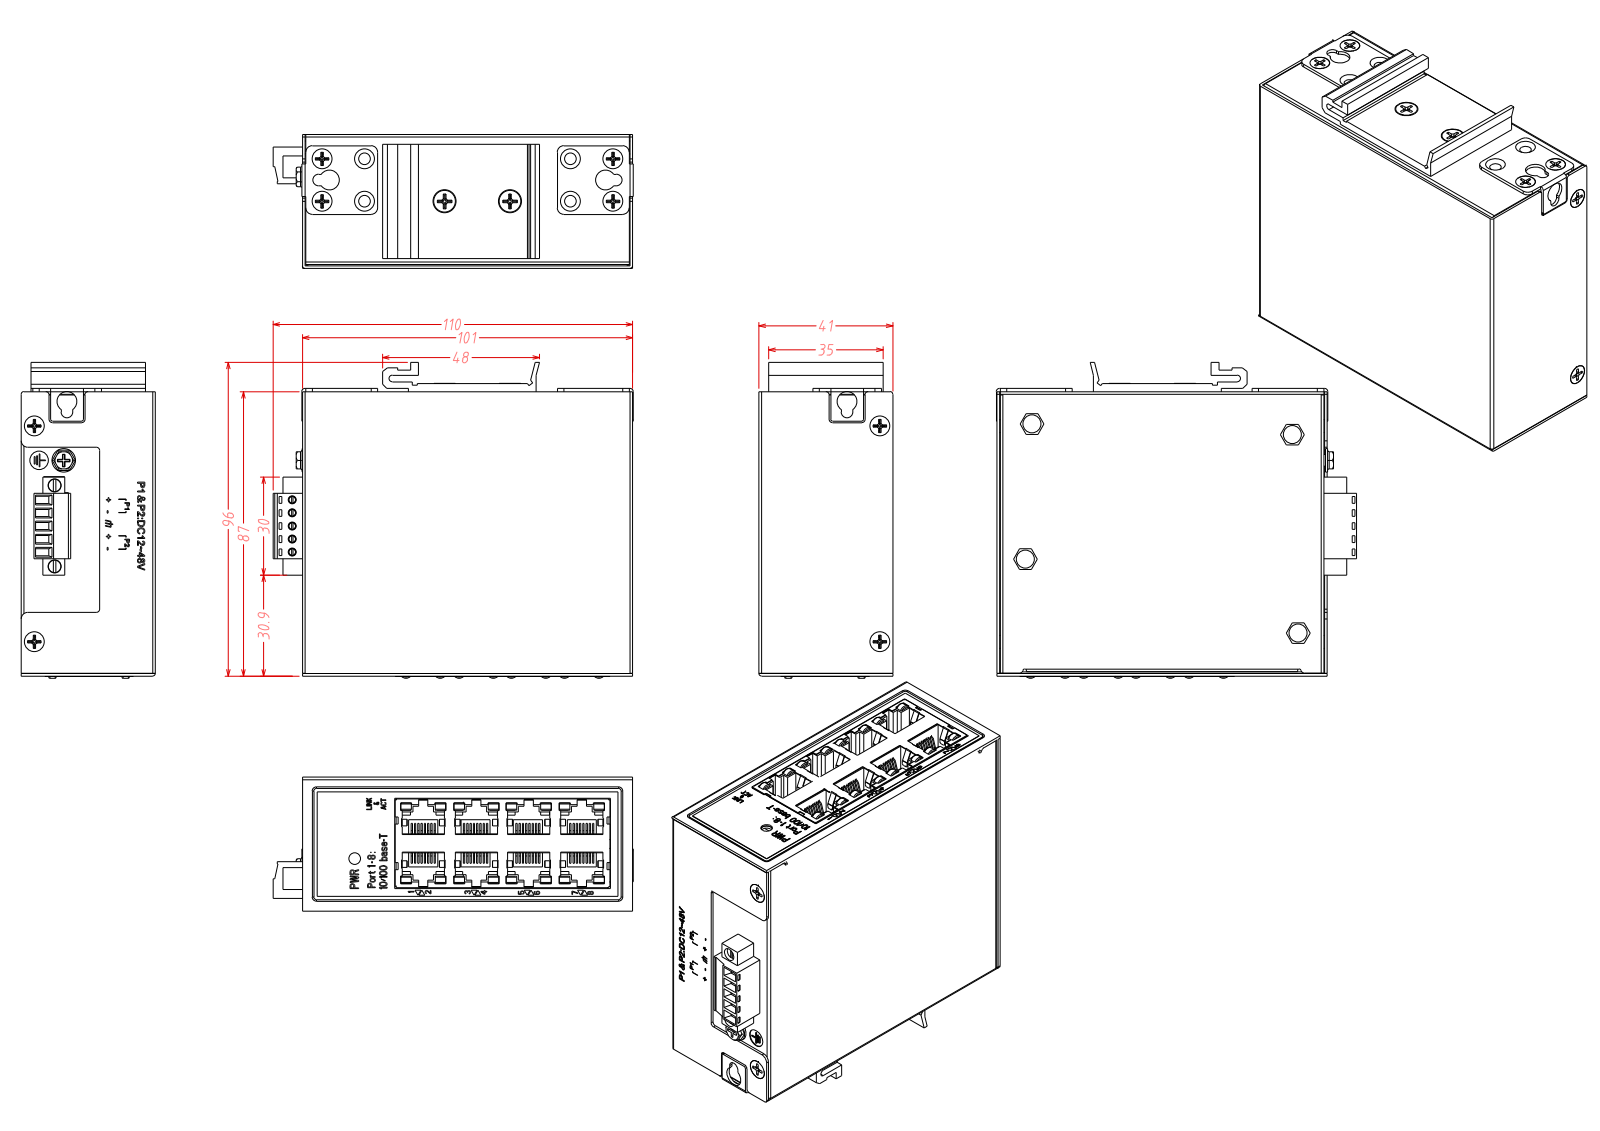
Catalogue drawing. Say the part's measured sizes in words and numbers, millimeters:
The part is named "PRT0123; PRT0124; PRT0125; PRT0126 (+8 more)". Its 3-D file was written by "PRO/ENGINEER BY PARAMETRIC TECHNOLOGY CORPORATION, 2011310 (CONFIG_CONTROL_DESIGN)". It is 41 solids with 3713 faces: 3101 planar, 418 cylindrical and 194 other. Overall it measures 110.2 by 96.68 by 41 millimeters. Its volume is 52 505 cubic millimeters and its surface area 104 092 square millimeters. Round holes: 13 of diameter 2.5, 5 of diameter 2.4, 4 of diameter 5.5, 3 of diameter 6, 2 of diameter 2.2, 2 of diameter 3.6, 2 of diameter 4, 1 of diameter 3.5, 1 of diameter 5.62. Round bosses or shafts: 9 of diameter 3.3, 6 of diameter 3.12, 5 of diameter 2.16, 5 of diameter 2.05, 5 of diameter 1, 5 of diameter 0.2, 4 of diameter 5.4, 2 of diameter 3.8. Partial cylindrical surfaces (rounded edges, fillets, slot ends): 16 of radius 0.2, 15 of radius 1, 13 of radius 0.8, 12 of radius 0.5, 10 of radius 2, 8 of radius 1.89, 6 of radius 0.48, 3 of radius 1.75. The main face-to-face distances are 0.8, 40.2, 1, 99.2, 41, 39.4, 1.8, 98.2, 100, 98.4. The hole center spacings are 4, 6.88, 8, 86.99, 12, 13, 89, 89.94.
